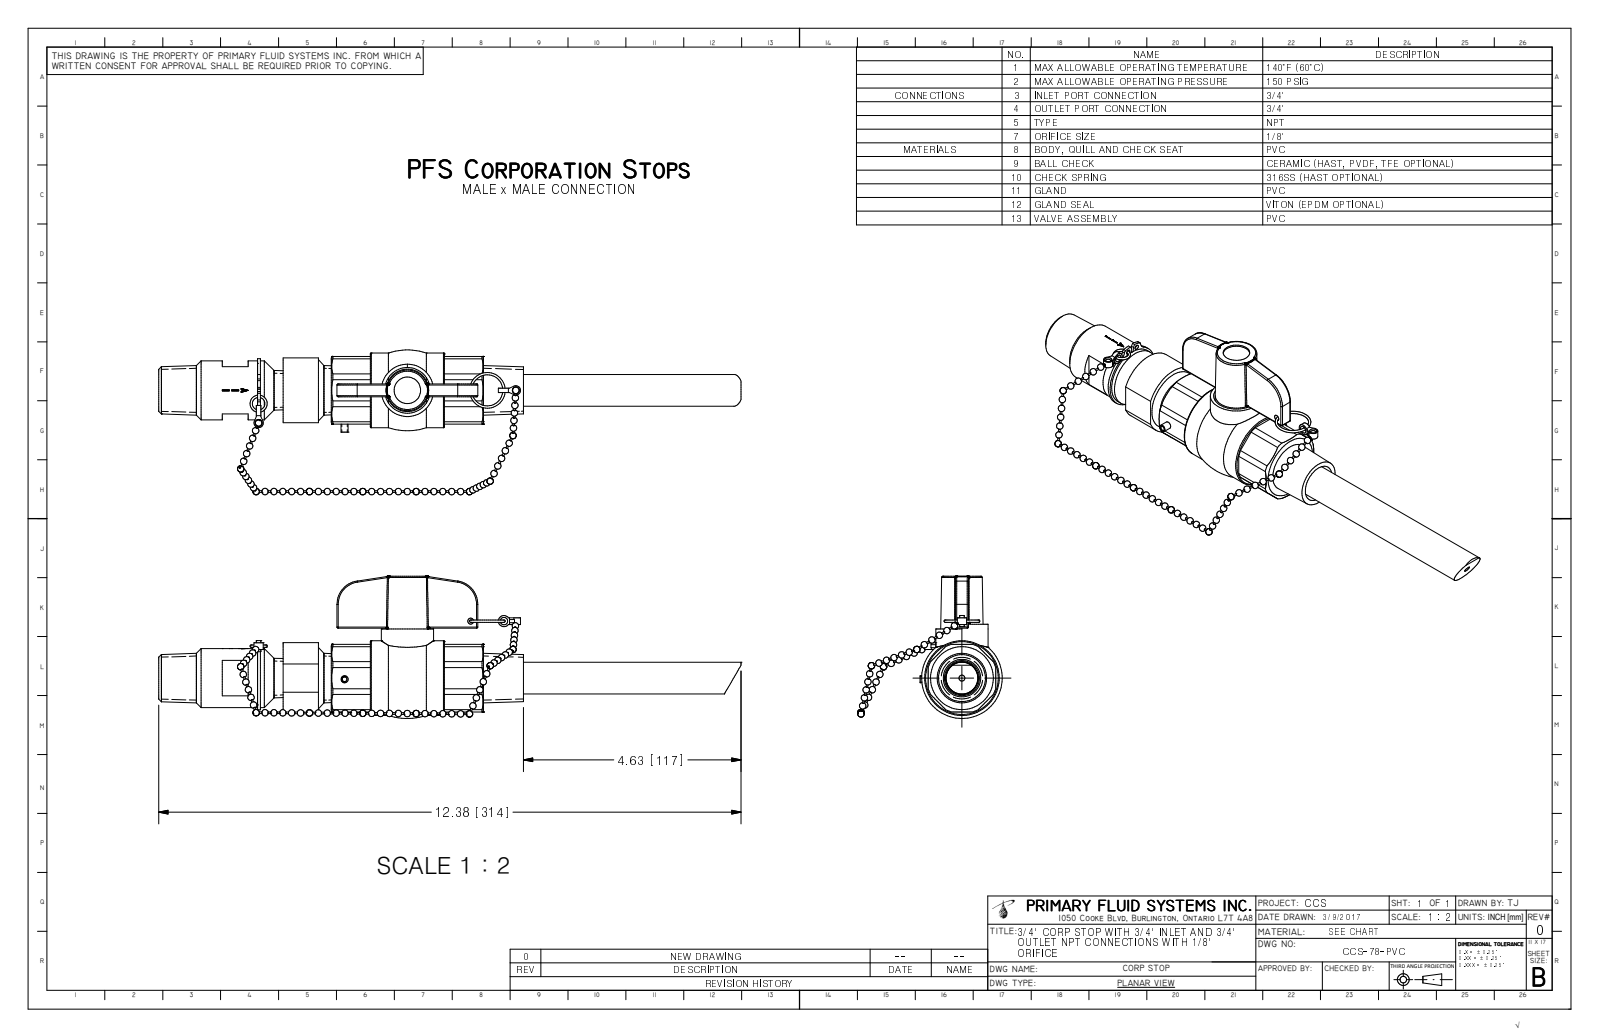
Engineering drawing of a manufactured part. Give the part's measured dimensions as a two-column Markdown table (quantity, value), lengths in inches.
| quantity | value |
| --- | --- |
| part name | CCS-78-PVC_R0 |
| STEP written by | Autodesk Inventor 2009 (AUTOMOTIVE_DESIGN) |
| units | inches |
| bodies | 1 solid, 396 faces (113 planar, 62 cylindrical, 221 other) |
| overall size | 12.38 × 3.073 × 3.016 |
| volume | 13.62 in³ |
| surface area | 73.71 in² |
| round holes (diameter × count) | 0.098 × 1, 0.125 × 1, 0.15 × 1, 0.25 × 1, 0.469 × 1, 0.56 × 1, 0.563 × 1, 0.97 × 1 |
| round bosses / shafts (diameter × count) | 1.585 × 1, 1.343 × 1, 1.25 × 1, 1.14 × 1, 1.11 × 1, 0.9 × 1, 0.675 × 1, 0.558 × 1 |
| partial cylindrical surfaces (radius × count) | 0.025 × 12, 0.054 × 2, 0.197 × 2, 0.5 × 2, 0.451 × 1, 0.563 × 1, 0.624 × 1, 0.75 × 1 |
| main face-to-face distances | 1.435, 0.55, 0.03, 0.275, 0.825, 0.187, 1.187, 0.363, 0.637, 0.217 |
| hole center spacings | 0.69 |
